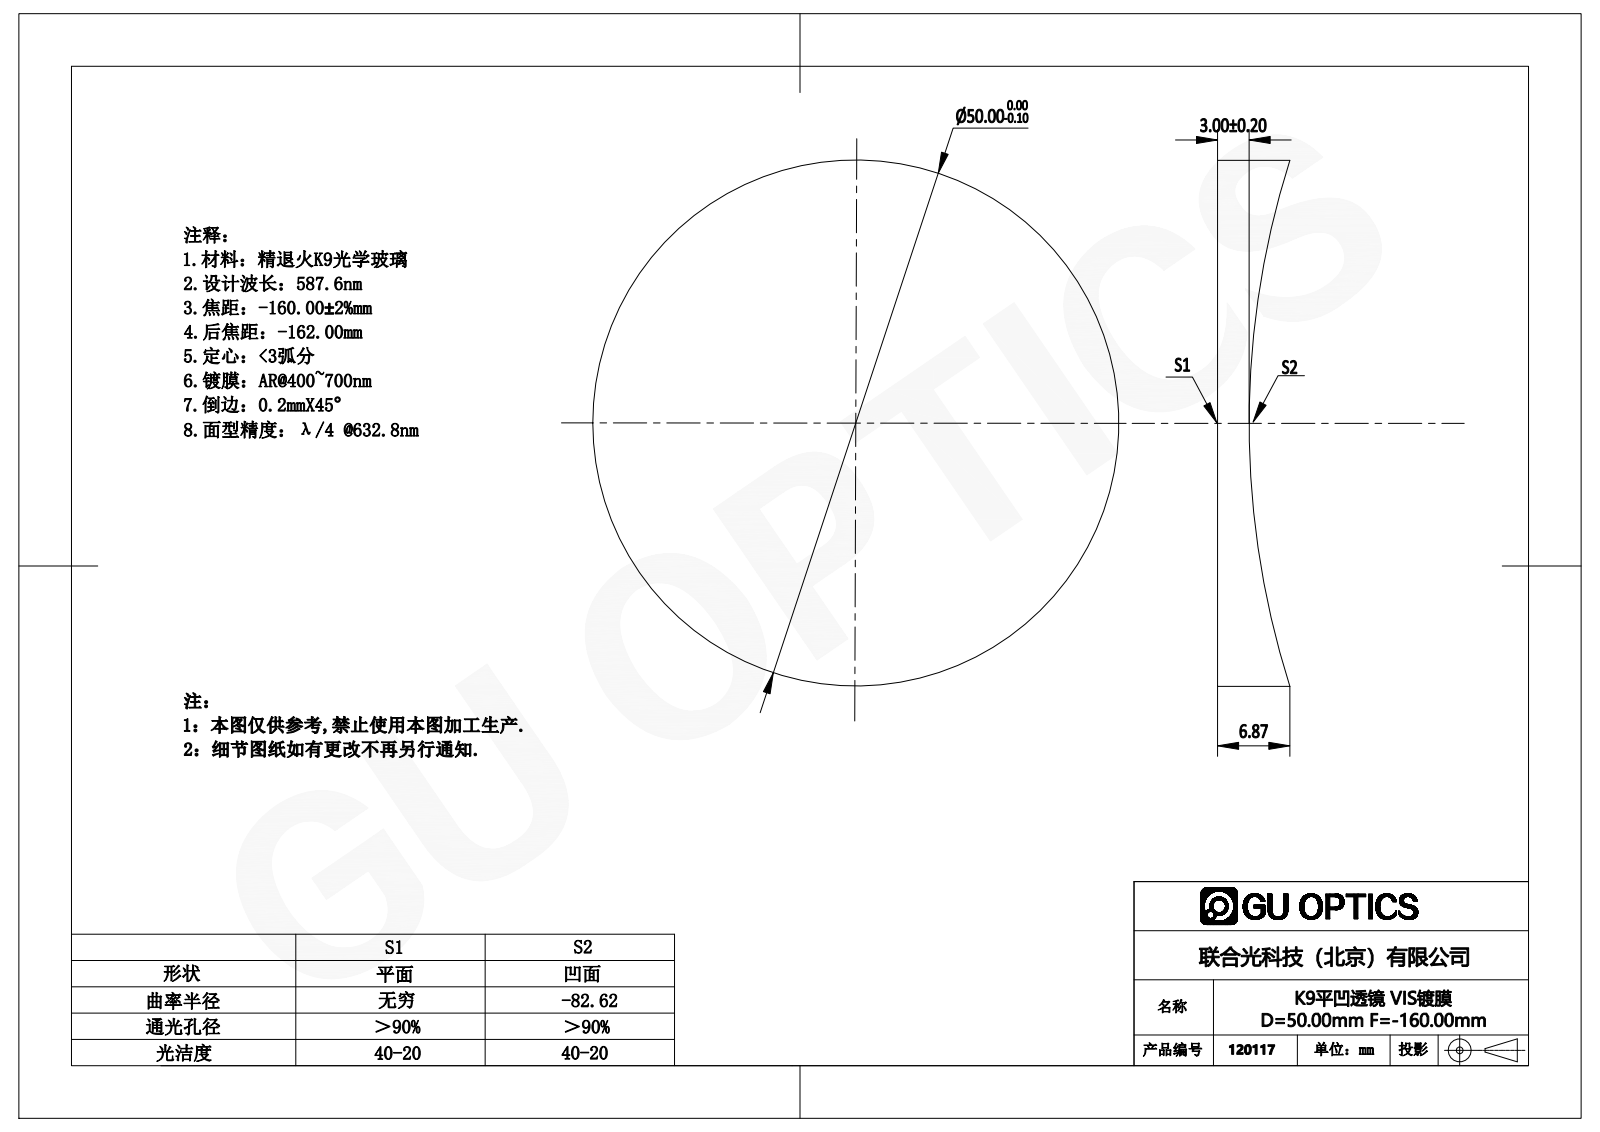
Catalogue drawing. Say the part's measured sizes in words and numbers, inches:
The part is named "120057". Its 3-D file was written by "SolidWorks 2016 (AUTOMOTIVE_DESIGN)". It is 1 solid with 5 faces: 1 planar, 2 cylindrical and 2 other. Overall it measures 1.969 by 1.969 by 0.27 inches. Its volume is 0.59 cubic inches and its surface area 7.834 square inches. Round bosses or shafts: 1 of diameter 1.969.
